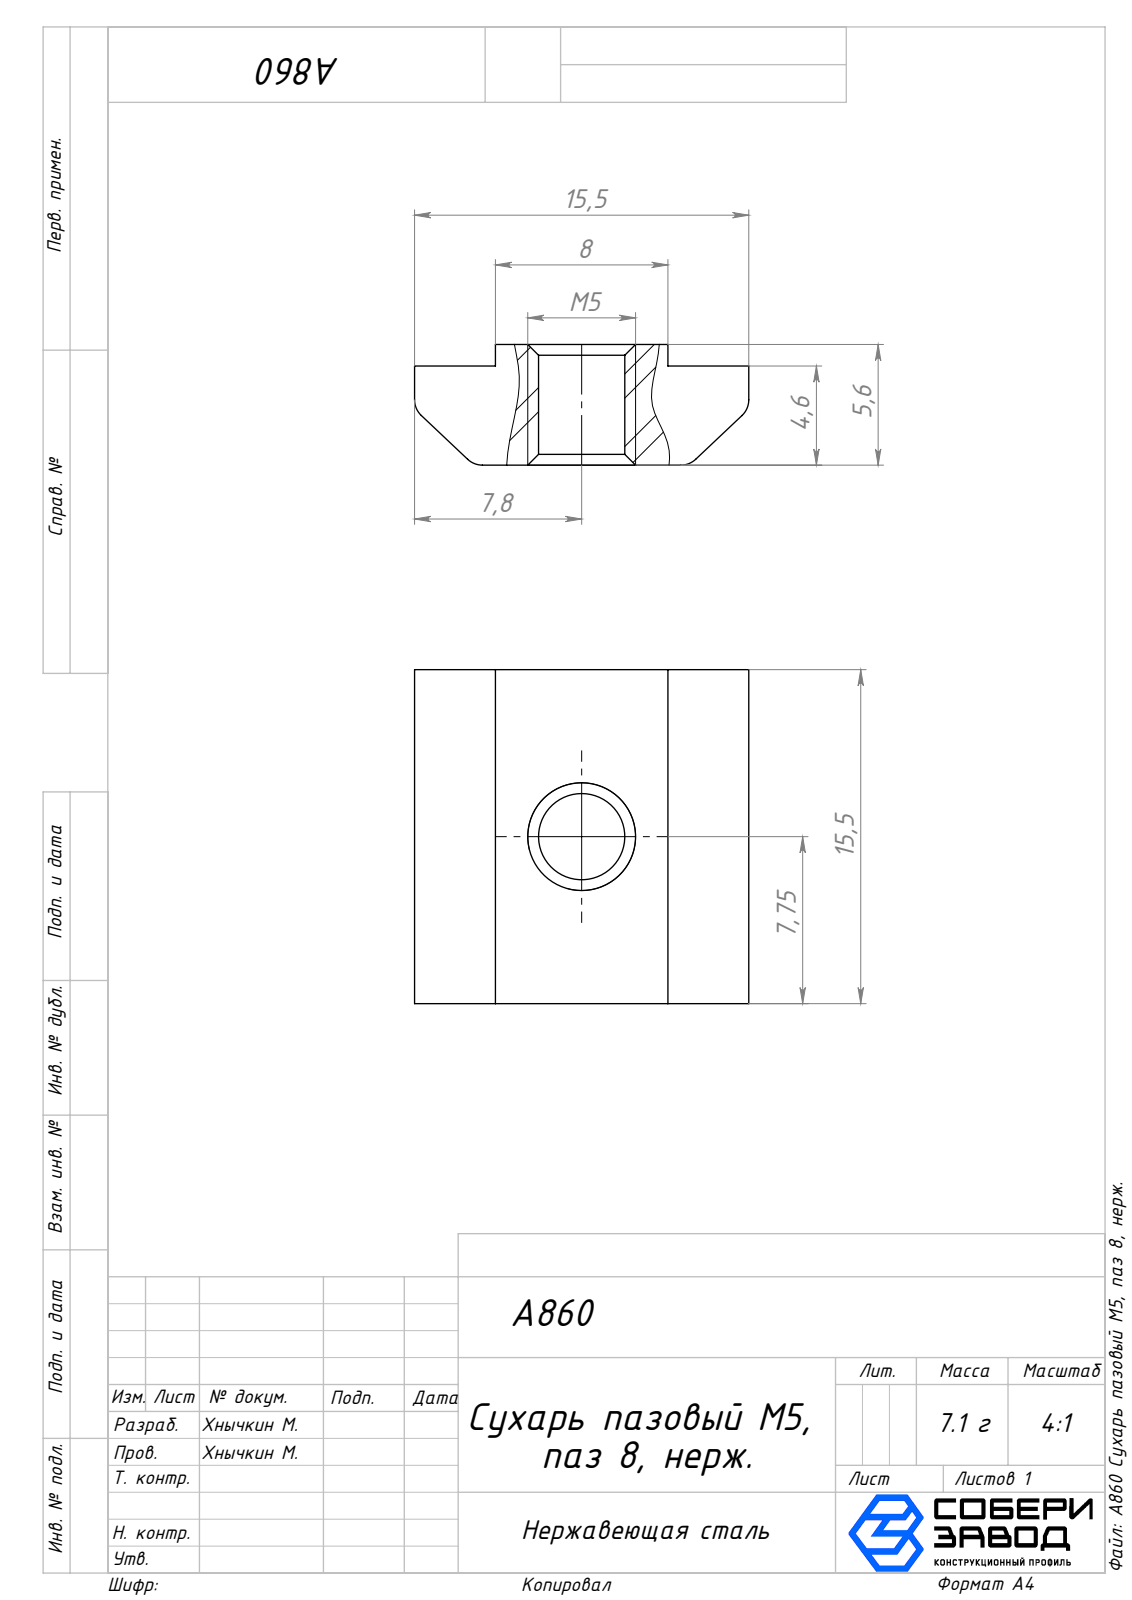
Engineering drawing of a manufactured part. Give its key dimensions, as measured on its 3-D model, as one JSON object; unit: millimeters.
{"part_name": "A860 Сухарь пазовый М5, паз 8, нерж.", "step_written_by": "SolidWorks 2025 (AUTOMOTIVE_DESIGN)", "units": "millimeters", "bodies": {"solids": 1, "faces": 22, "planar": 12, "cylindrical": 6, "other": 4}, "overall_size": [15.5, 15.5, 5.6], "volume_mm3": 1043, "surface_area_mm2": 786, "round_holes": [[4, 1]], "partial_cylinders_radius": [[1, 4]], "face_to_face_distances": [4.6, 5.6, 1, 15.5, 3.75, 11.75, 8]}
